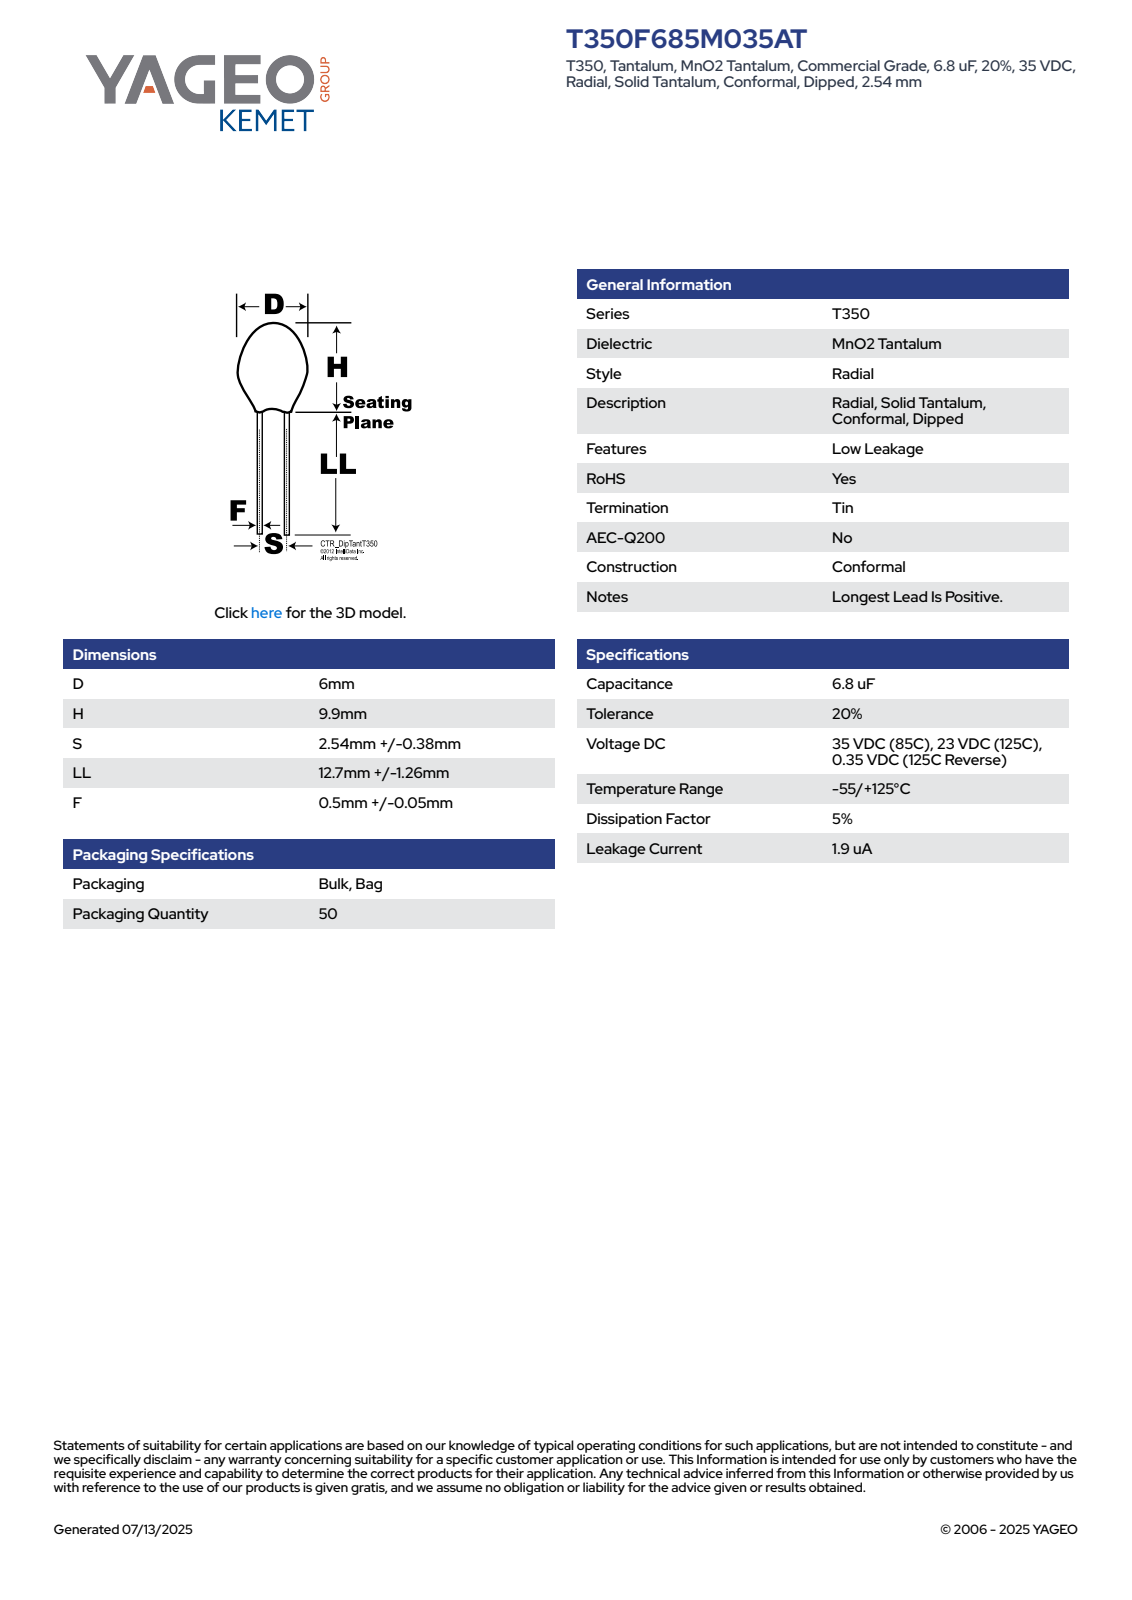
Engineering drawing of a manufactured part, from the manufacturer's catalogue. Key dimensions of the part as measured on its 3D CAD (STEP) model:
Part name (STEP PRODUCT): CTR_T350_D6H9.9S2.54LL13.96F0.55
STEP written by: SolidWorks 2014 (AUTOMOTIVE_DESIGN)
Units: millimetres
Bodies: 1 solid, 73 faces (26 planar, 10 cylindrical, 37 other)
Overall size (bounding box): 23.86 × 6 × 6
Volume: 239 mm³ · Surface area: 246 mm²
Round bosses / shafts (diameter × count): ⌀0.55 ×2, ⌀6 ×1
Partial cylindrical surfaces — rounded edges, fillets, slot ends (radius × count): R2.99 ×1
Main face-to-face distances: 9.9, 13.96, 23.86, 19.44, 5.48, 4.42, 18.44, 4.48, 1, 5.42
